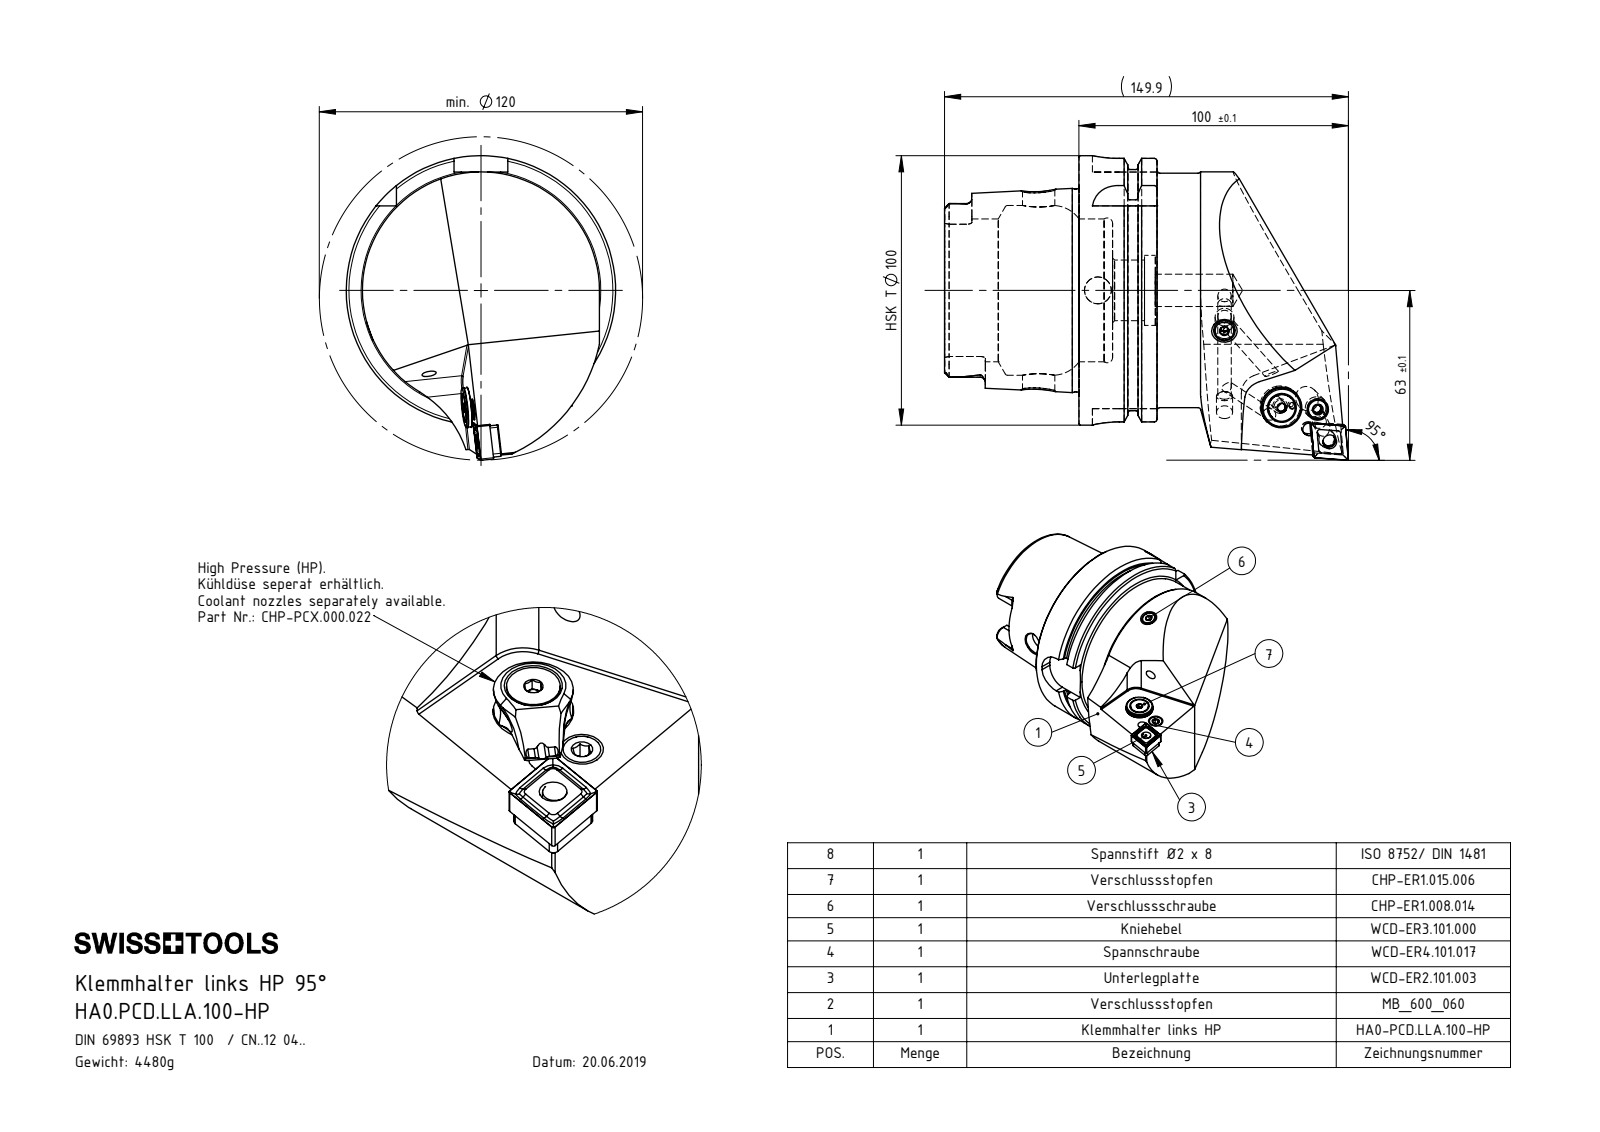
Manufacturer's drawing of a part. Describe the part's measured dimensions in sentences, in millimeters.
The part is named "HA0.PCD.LLA.100-HP; CNMG120404; CHP-ER1.015.006; DIN 7991 - M5x15 (+8 more)". Its 3-D file was written by "SolidWorks 2017 (AUTOMOTIVE_DESIGN)". It is 12 solids with 373 faces: 155 planar, 90 cylindrical and 128 other. Overall it measures 149.9 by 113 by 100 millimeters. Its volume is 572 719 cubic millimeters and its surface area 75 052 square millimeters. Round holes: 4 of diameter 5, 2 of diameter 4.2, 2 of diameter 7, 2 of diameter 12, 1 of diameter 1.2, 1 of diameter 2, 1 of diameter 2.5, 1 of diameter 3, 1 of diameter 5.16, 1 of diameter 5.2, 1 of diameter 6, 1 of diameter 6.4. Round bosses or shafts: 2 of diameter 8, 1 of diameter 100, 1 of diameter 91.95, 1 of diameter 87, 1 of diameter 75.26, 1 of diameter 15, 1 of diameter 13.4, 1 of diameter 10. Partial cylindrical surfaces (rounded edges, fillets, slot ends): 6 of radius 1.9, 4 of radius 0.4, 4 of radius 1, 4 of radius 10, 2 of radius 0.5, 2 of radius 2.5, 2 of radius 4.83, 2 of radius 4.88. The main face-to-face distances are 12.45, 28.95, 16.5, 49.9, 62.35, 78.85, 87.8, 78.2, 28.3, 15.85. The hole center spacings are 4.5, 4.51, 9.18, 13.67, 22.21, 22.27, 2.24, 2.26.
